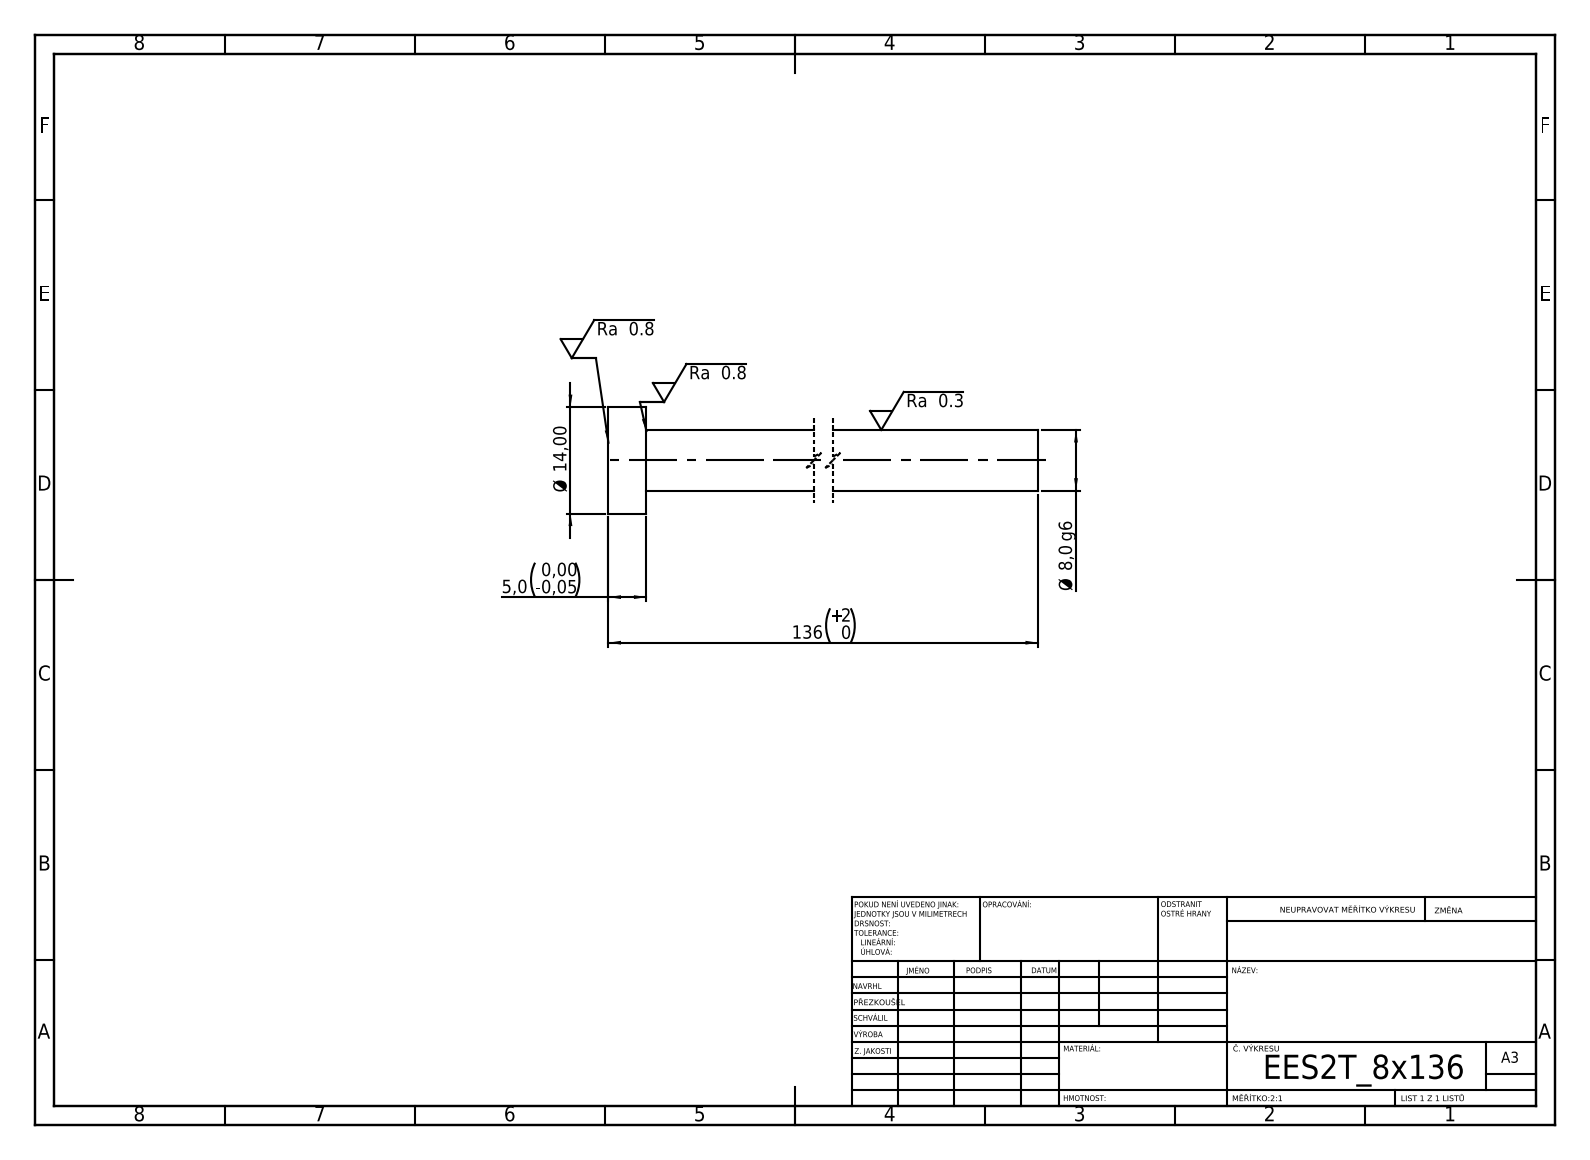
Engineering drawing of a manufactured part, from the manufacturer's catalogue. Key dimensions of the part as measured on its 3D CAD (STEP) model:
STEP written by: SolidWorks 2019 (CONFIG_CONTROL_DESIGN)
Units: millimetres
Bodies: 1 solid, 7 faces (3 planar, 4 cylindrical, 0 other)
Overall size (bounding box): 136 × 14 × 14
Volume: 7 354 mm³ · Surface area: 3 820 mm²
Round bosses / shafts (diameter × count): ⌀14 ×1, ⌀8 ×1
Main face-to-face distances: 5, 136, 131
